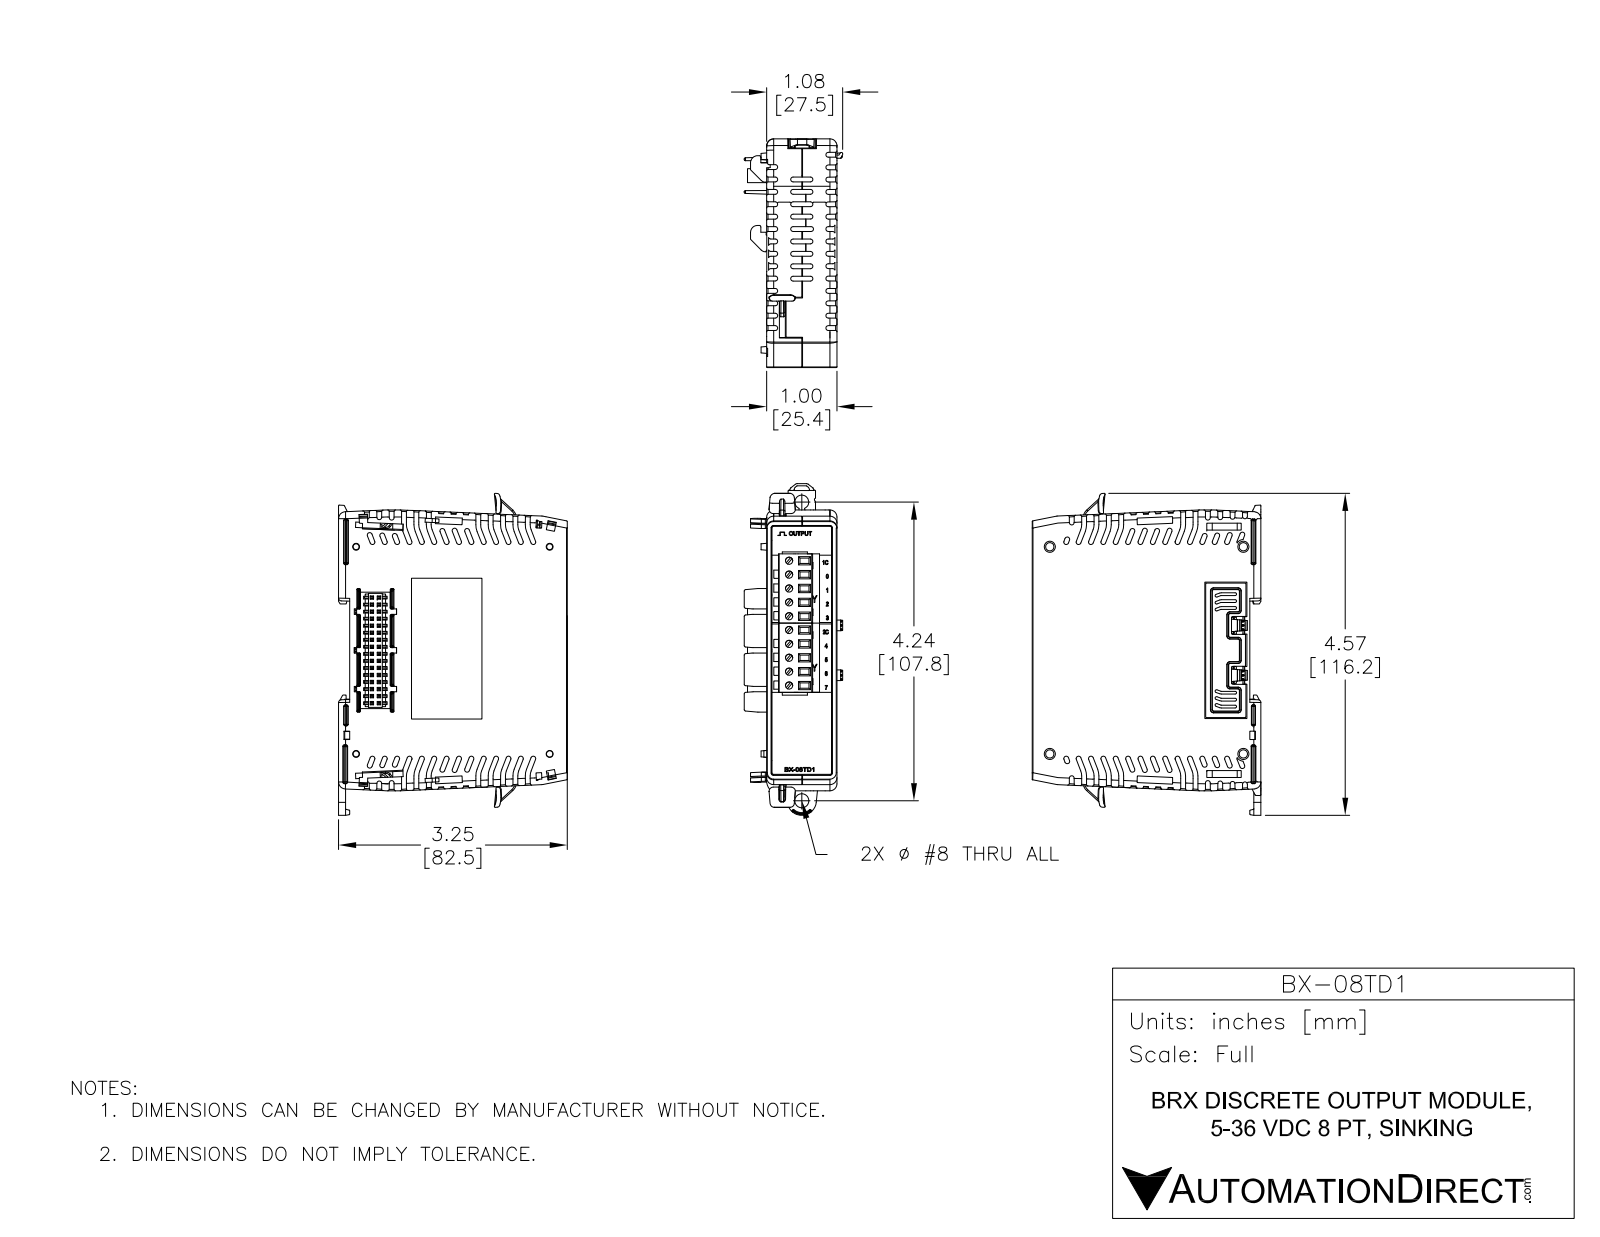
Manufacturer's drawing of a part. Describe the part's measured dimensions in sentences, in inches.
The part is named "BX-08TD1". Its 3-D file was written by "SolidWorks 2017 (AUTOMOTIVE_DESIGN)". It is 22 solids with 3582 faces: 2541 planar, 563 cylindrical and 478 other. Overall it measures 4.586 by 3.311 by 1.402 inches. Its volume is 11.59 cubic inches and its surface area 72.76 square inches. Round holes: 2 of diameter 0.047, 2 of diameter 0.065, 2 of diameter 0.118, 2 of diameter 0.118, 1 of diameter 0.199. Round bosses or shafts: 2 of diameter 0.062, 2 of diameter 0.059. Partial cylindrical surfaces (rounded edges, fillets, slot ends): 102 of radius 0.005, 47 of radius 0.01, 34 of radius 0.02, 24 of radius 0.005, 21 of radius 0.008, 14 of radius 0.117, 13 of radius 0.039, 12 of radius 0.01. The main face-to-face distances are 1, 3.211, 3.22, 0.475, 0.1, 0.157, 3.053, 3.063, 0.787, 0.63. The hole center spacings are 0.1, 0.824, 0.919, 1.3, 2.093, 2.193, 2.585, 2.617.
